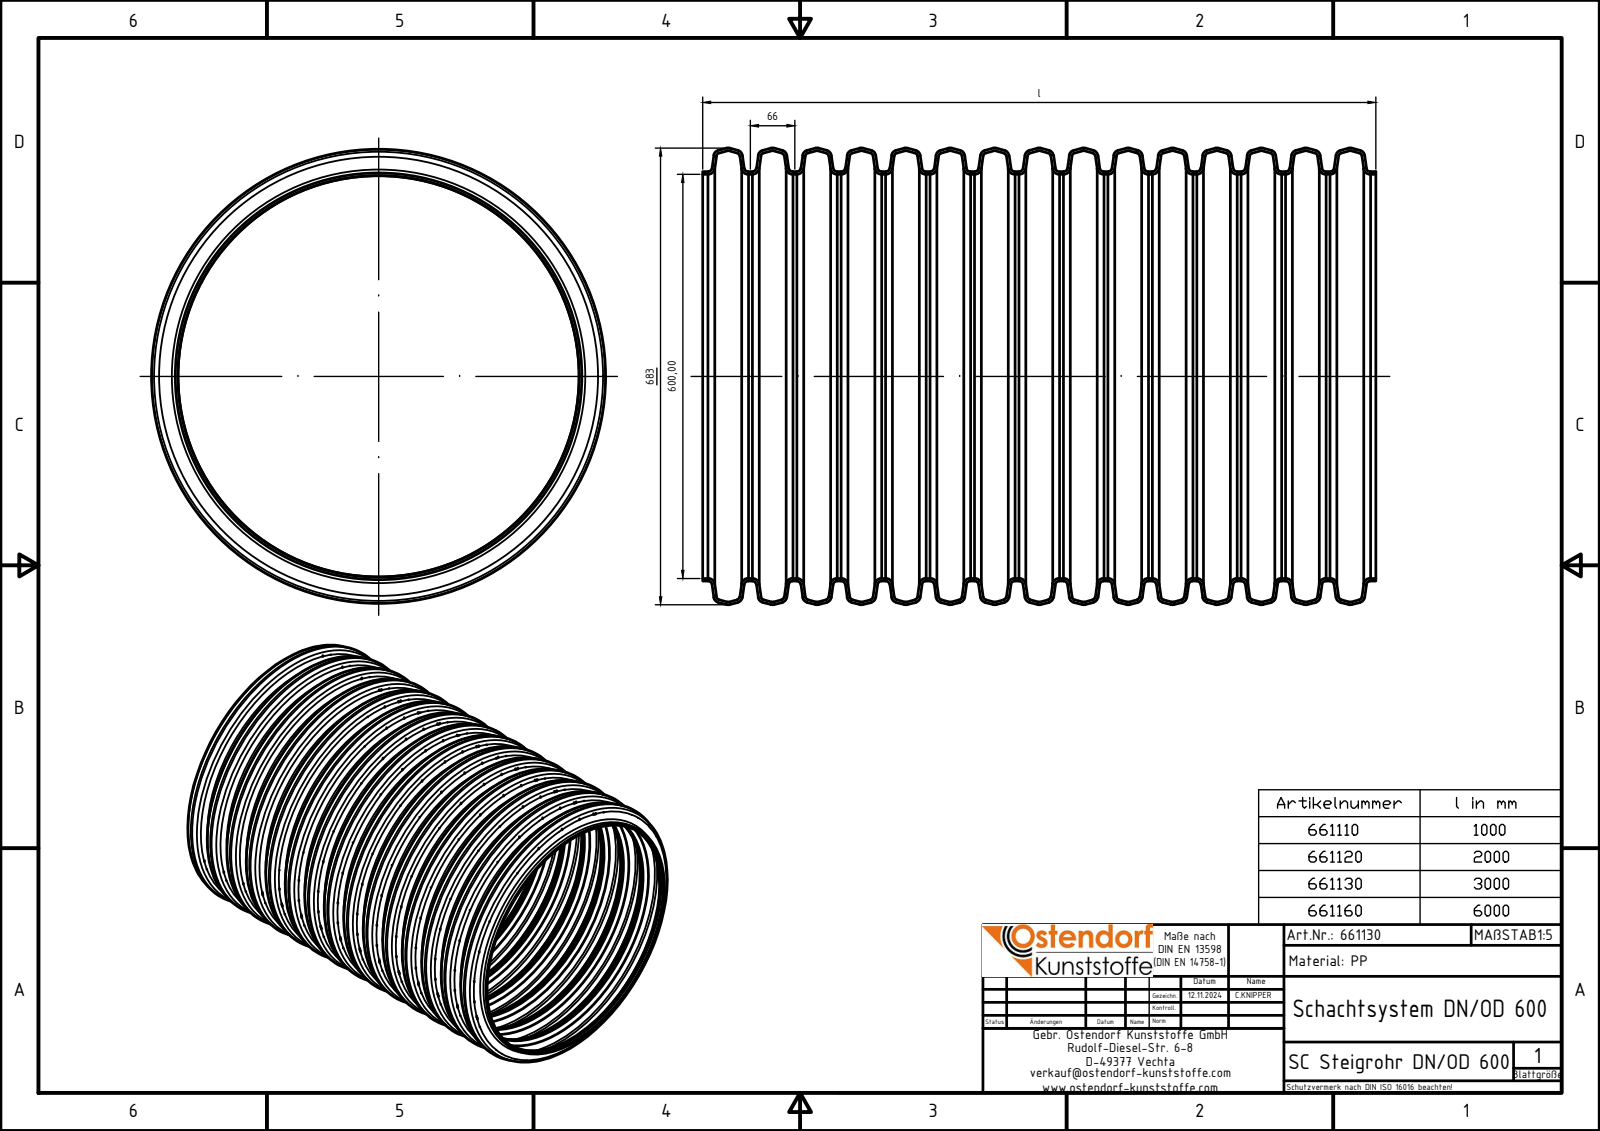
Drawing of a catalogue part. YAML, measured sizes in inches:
part_name: "661130z"
step_written_by: "Autodesk Inventor 2024 (AUTOMOTIVE_DESIGN)"
units: inches
bodies: {solids: 1, faces: 904, planar: 2, cylindrical: 92, other: 810}
overall_size: [118.11, 26.707, 26.707]
volume: 2518
surface_area: 32010
round_holes:
  - {diameter: 23.622, count: 1}
  - {diameter: 23.622, count: 1}
  - {diameter: 23.622, count: 1}
  - {diameter: 23.622, count: 1}
  - {diameter: 23.622, count: 1}
round_bosses_or_shafts:
  - {diameter: 23.936, count: 1}
  - {diameter: 23.936, count: 1}
  - {diameter: 23.936, count: 1}
  - {diameter: 23.936, count: 1}
  - {diameter: 23.936, count: 1}
  - {diameter: 23.935, count: 1}
  - {diameter: 23.935, count: 1}
  - {diameter: 23.934, count: 1}
face_to_face_distances: [118.11]
